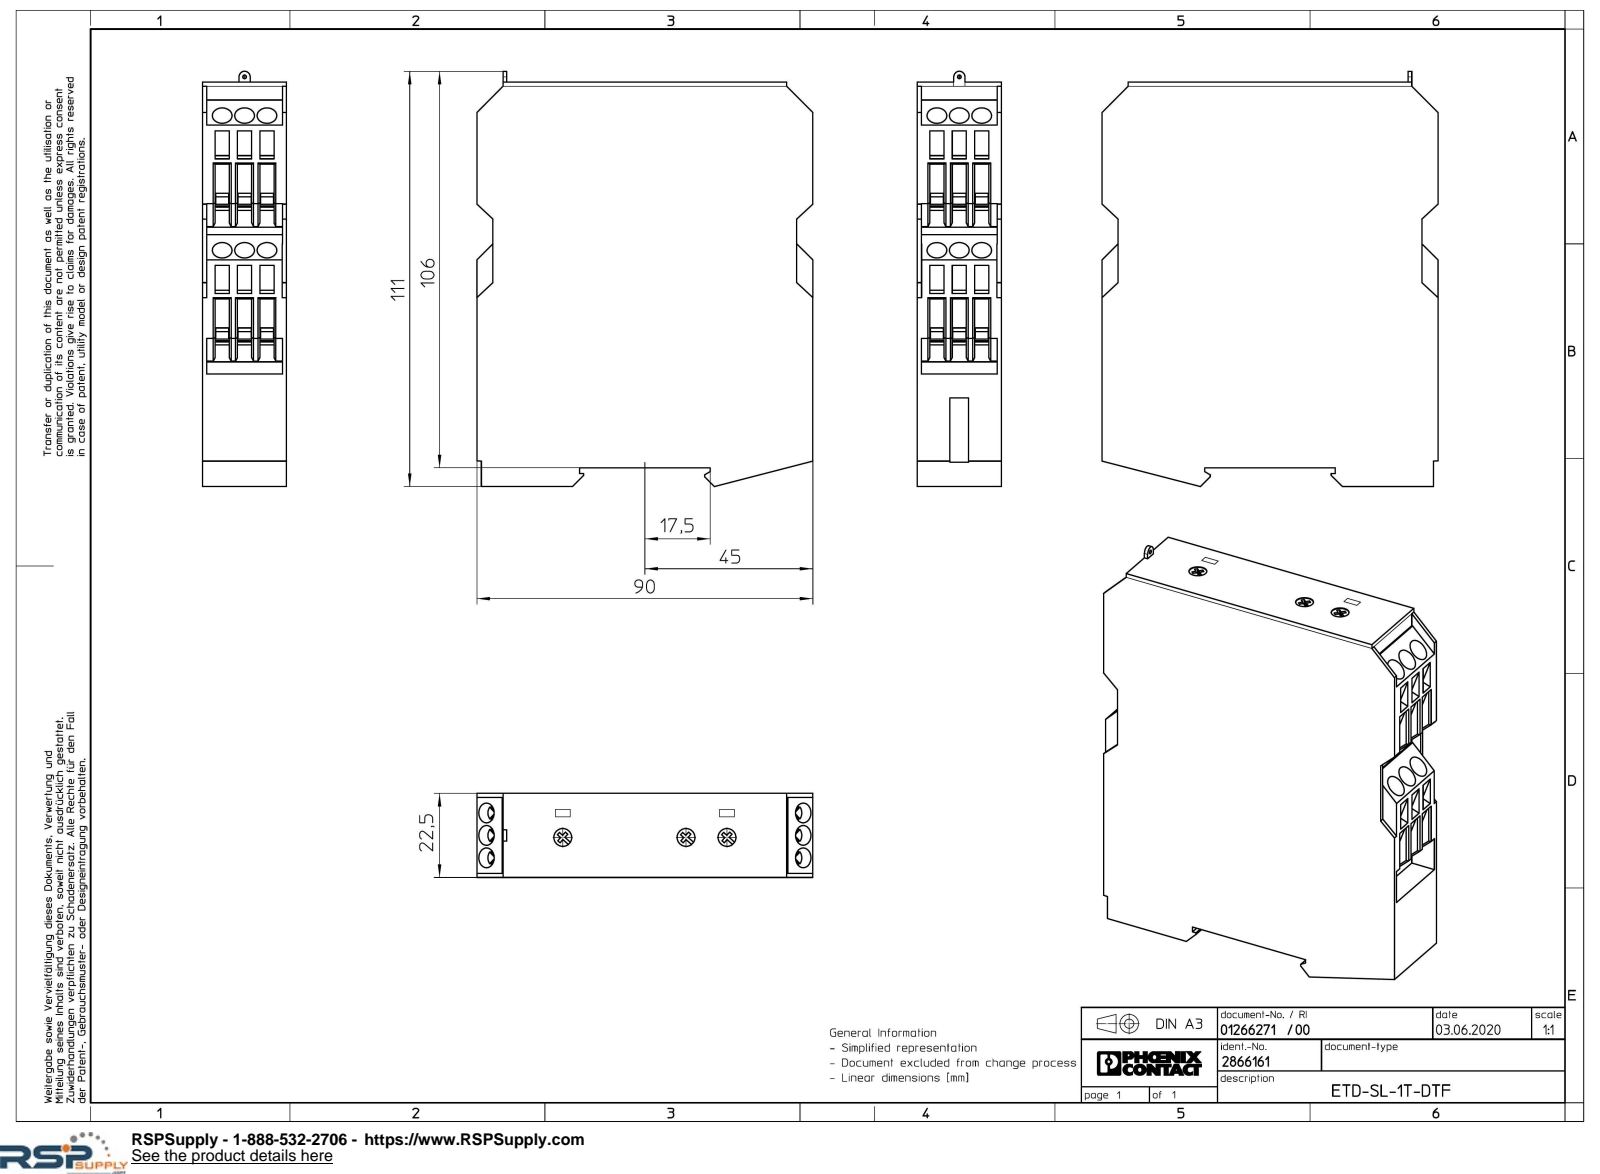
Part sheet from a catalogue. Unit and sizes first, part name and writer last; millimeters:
Units: millimetres
Overall size (bounding box): 111 × 90 × 22.5
Round holes (diameter × count): ⌀5.3 ×12, ⌀4.8 ×3, ⌀1 ×1
Partial cylindrical surfaces — rounded edges, fillets, slot ends (radius × count): R1.5 ×1
Main face-to-face distances: 22.5, 6, 90, 12, 103.15, 3.8, 7, 3.5, 2.2, 3.65
Hole centre spacings: 6, 12.31, 12, 13.69, 13.7, 17.19, 11, 33
Volume: 198 351 mm³ · Surface area: 33 719 mm²
Bodies: 1 solid, 635 faces (584 planar, 33 cylindrical, 18 other)
Part name (STEP PRODUCT): ETD-SL-1T-DTF-400-select
STEP written by: Creo Elements/Direct Modeling 20.1A 29-Sep-2018 (C) Parametric Technology GmbH (AUTOMOTIVE_DESIGN)
